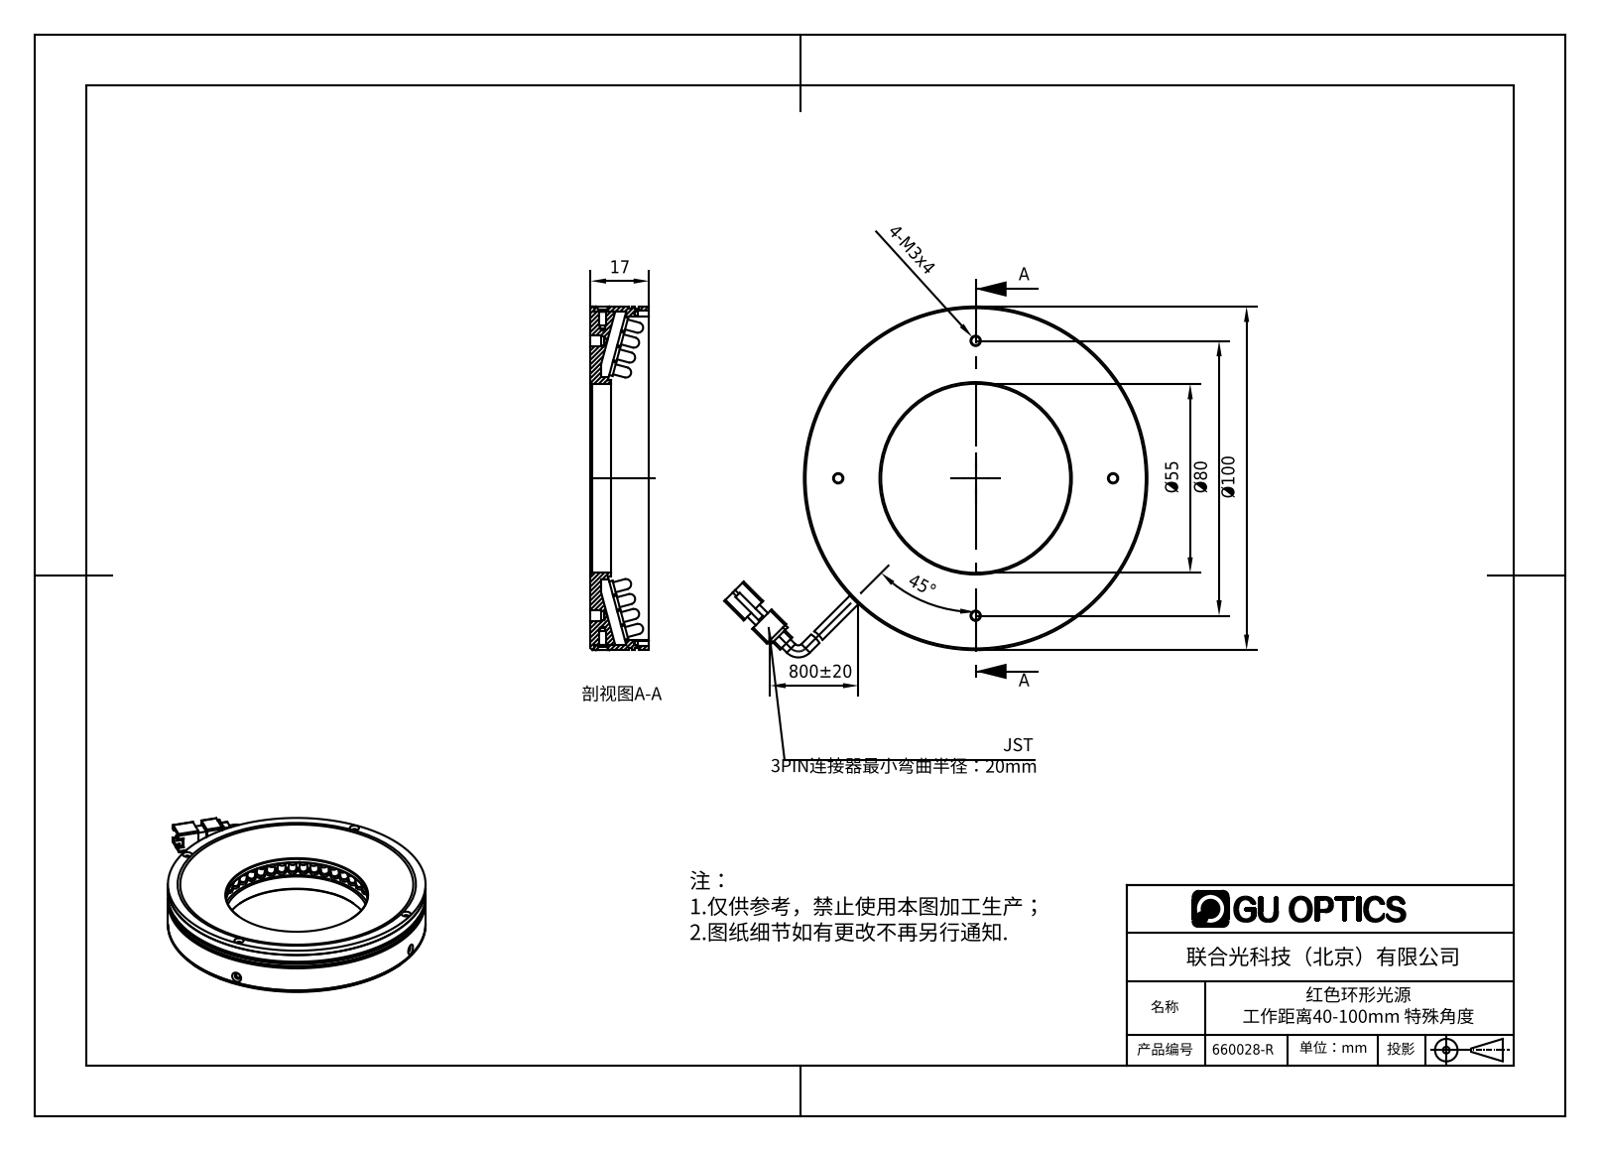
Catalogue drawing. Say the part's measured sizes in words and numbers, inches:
The part is named "660028-R". Its 3-D file was written by "SolidWorks 2016 (AUTOMOTIVE_DESIGN)". It is 216 solids with 3870 faces: 2609 planar, 980 cylindrical and 281 other. Overall it measures 4.85 by 4.021 by 0.884 inches. Its volume is 3.55 cubic inches and its surface area 106.7 square inches. Round holes: 6 of diameter 0.063, 4 of diameter 0.049, 4 of diameter 0.067, 4 of diameter 0.098, 4 of diameter 0.118, 4 of diameter 0.138, 2 of diameter 0.079, 2 of diameter 0.094, 1 of diameter 2.165, 1 of diameter 3.701. Round bosses or shafts: 210 of diameter 0.15, 210 of diameter 0.118, 2 of diameter 0.138, 1 of diameter 3.937, 1 of diameter 3.898, 1 of diameter 3.819, 1 of diameter 2.323, 1 of diameter 2.244. Partial cylindrical surfaces (rounded edges, fillets, slot ends): 10 of radius 0.02, 4 of radius 0.039, 1 of radius 0.065, 1 of radius 0.295. The main face-to-face distances are 0.039, 0.079, 0.669, 0.118, 0.63, 0.02, 0.748, 0.551, 0.709, 0.197. The hole center spacings are 2.46, 0.315, 1.575, 1.89, 2.227, 2.672, 3.465, 3.15.
